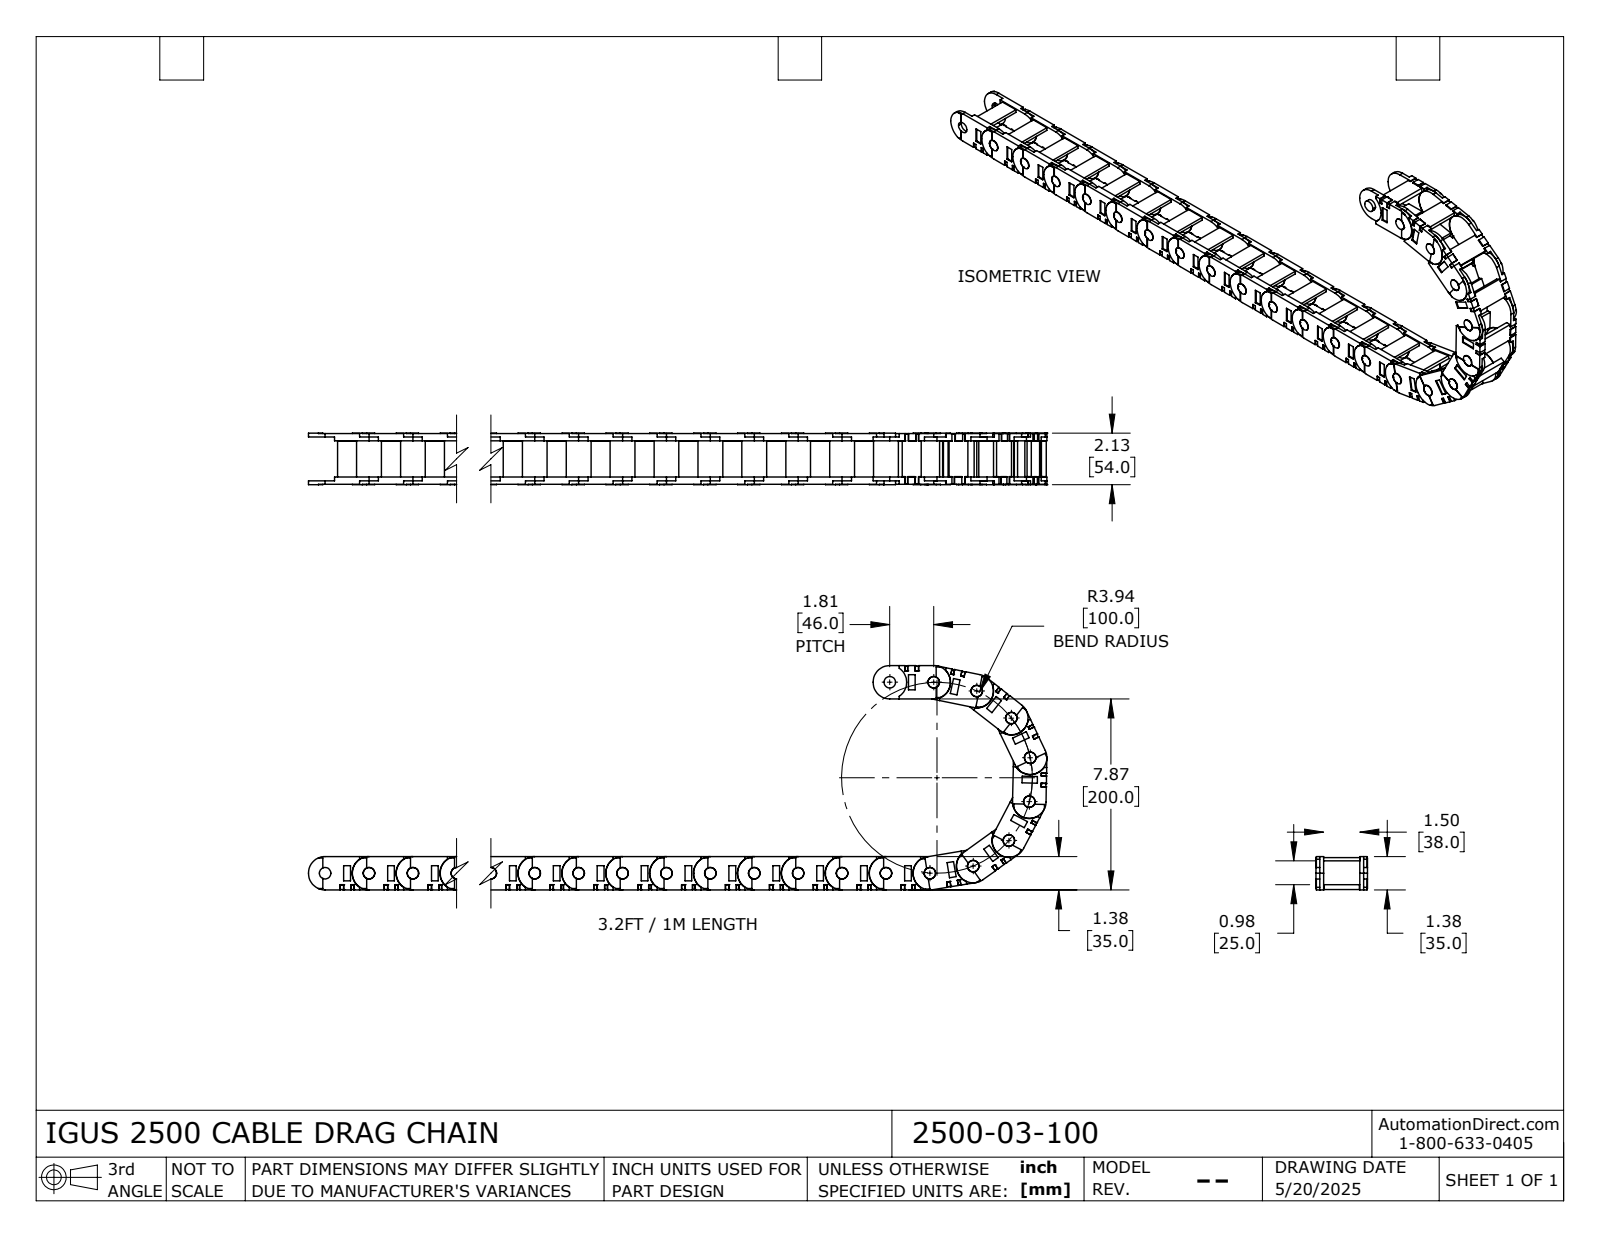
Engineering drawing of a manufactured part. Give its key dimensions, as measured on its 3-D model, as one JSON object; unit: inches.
{"part_name": "2500_03_100", "step_written_by": "SolidWorks 2024 (AUTOMOTIVE_DESIGN)", "units": "inches", "bodies": {"solids": 66, "faces": 2398, "planar": 1870, "cylindrical": 528, "other": 0}, "overall_size": [30.87, 9.252, 2.126], "volume_in3": 40.89, "surface_area_in2": 601.2, "round_holes": [[0.473, 22]], "round_bosses_or_shafts": [[0.472, 22], [1.378, 21]], "partial_cylinders_radius": [[0.697, 23], [0.689, 2]], "face_to_face_distances": [0.157, 1.654, 1.811, 0.142, 0.299, 1.795, 1.953, 1.496, 0.016, 2.094], "hole_center_spacings": [1.811, 3.622, 5.433, 7.244, 9.055, 10.866, 12.677, 14.488]}
